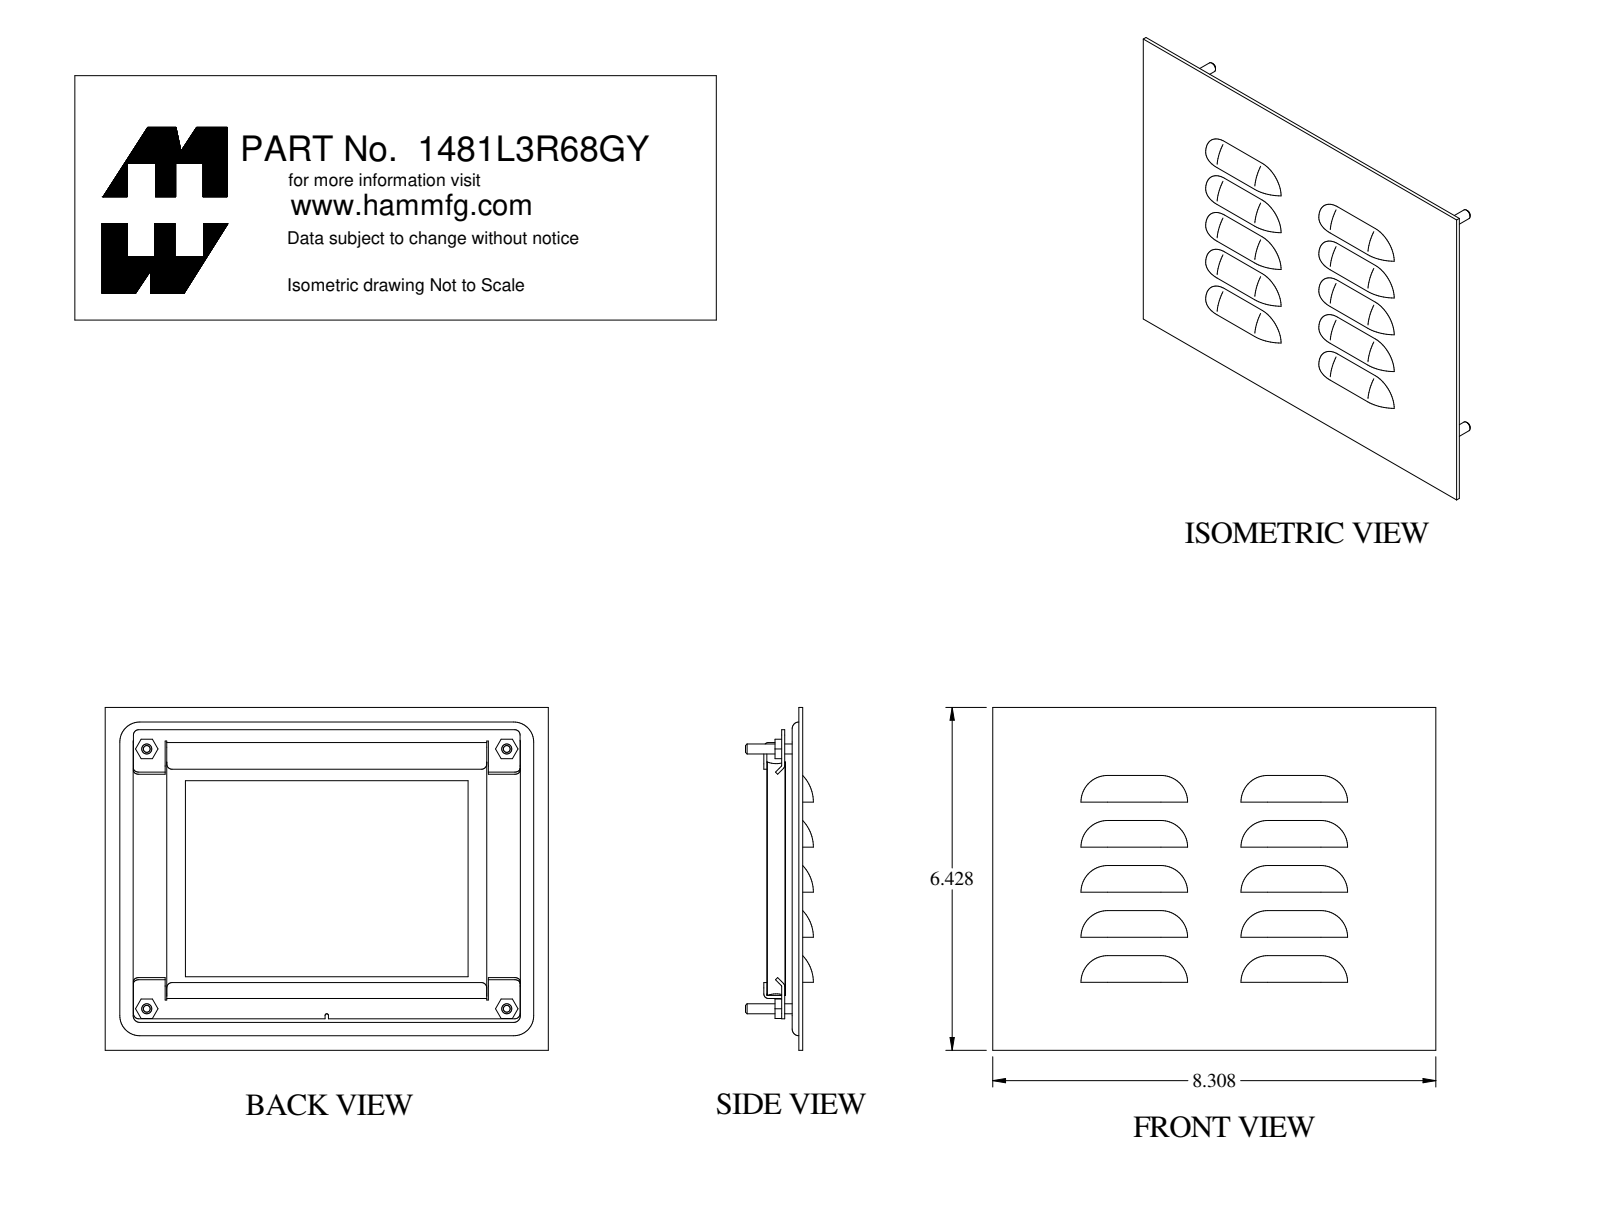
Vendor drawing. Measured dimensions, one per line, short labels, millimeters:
name: 1481L3R68GY
written by: SolidWorks 2021 (AUTOMOTIVE_DESIGN)
unit: mm
bodies: 13 solids, 314 faces (155 planar, 99 cylindrical, 60 other)
size: 211 × 163.3 × 32.3
volume: 206 100 mm³; area: 154 500 mm²
holes: 4× ⌀4, 4× ⌀5.6
bosses: 4× ⌀6.4, 4× ⌀4.8
rounds: 12× R2.5, 6× R0.7, 6× R2.2, 5× R16.6, 5× R18.4, 4× R3.2, 4× R3.2, 4× R9.5
face distances: 1.8, 7.6, 6.4, 9.4, 15.8, 14, 1.3, 8.2, 17.1, 15.2
hole spacings: 123.7, 171.5, 211.4
